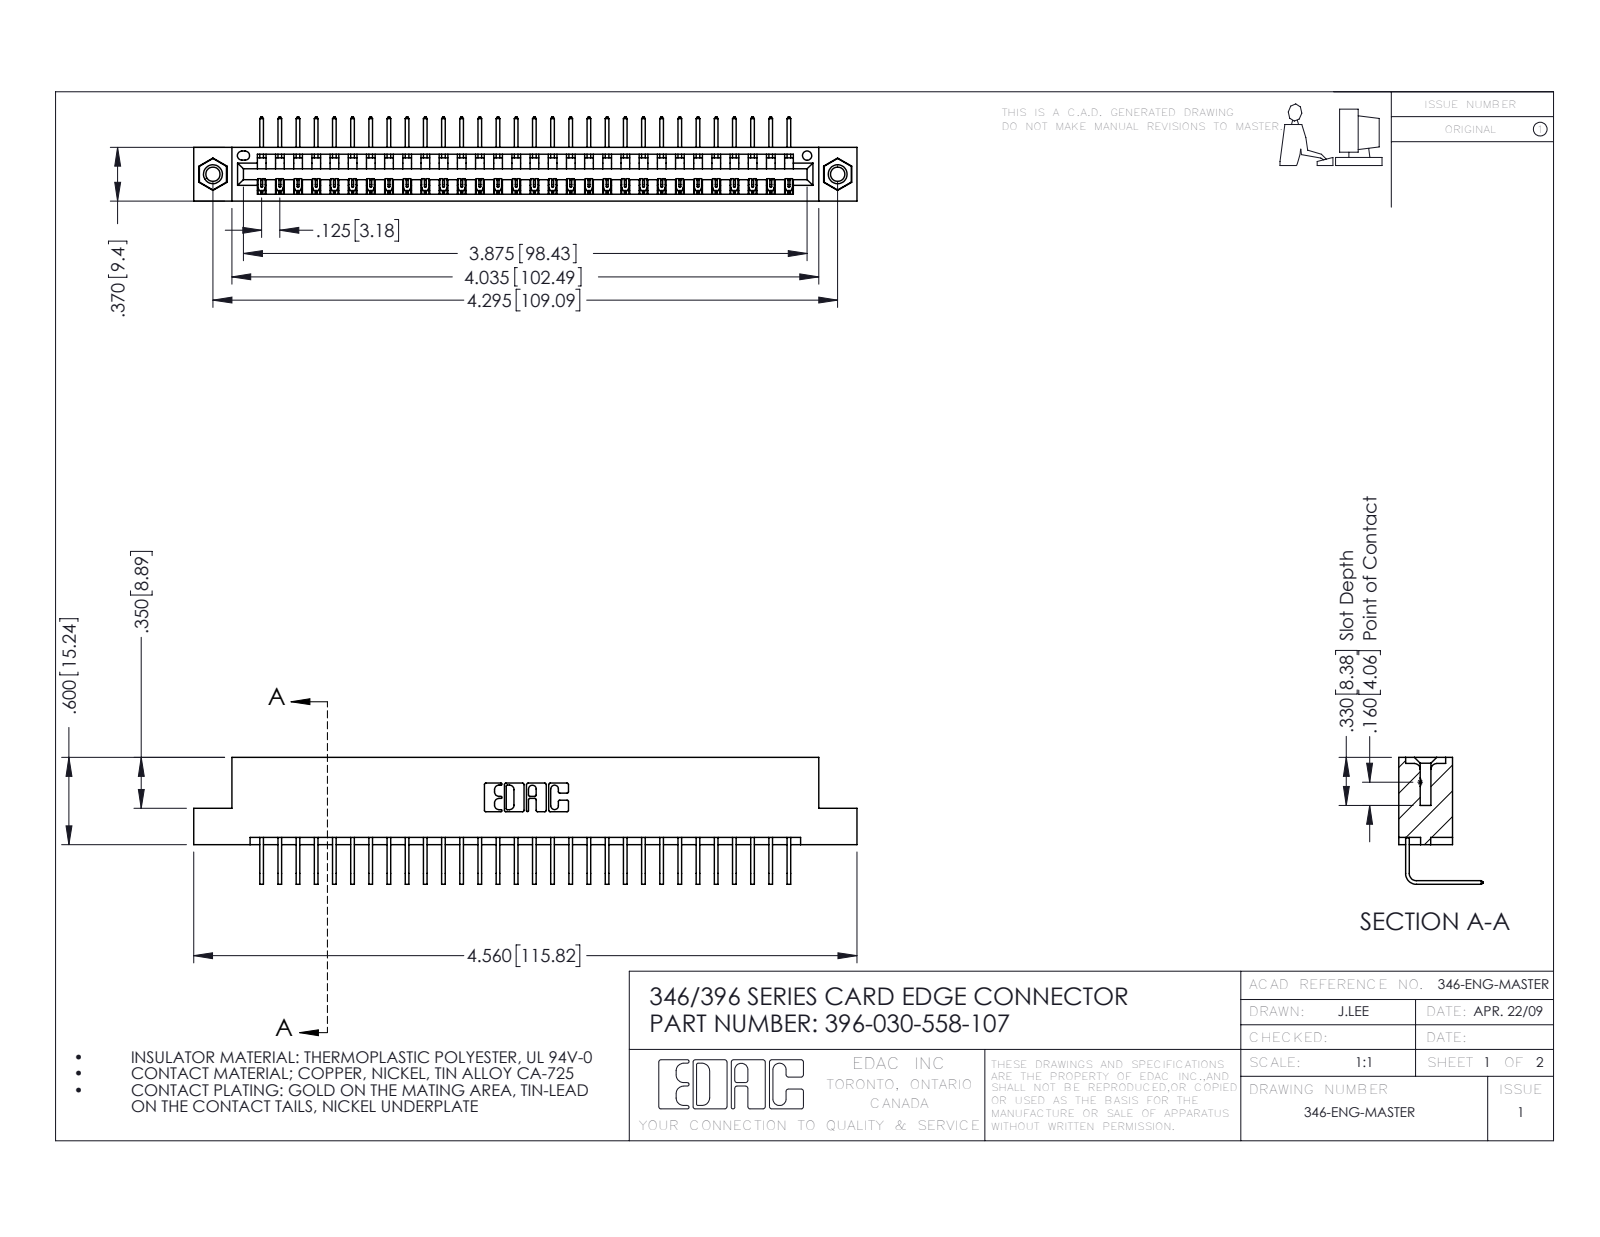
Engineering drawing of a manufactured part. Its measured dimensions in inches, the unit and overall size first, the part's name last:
Units: inches
Overall size (bounding box): 4.56 × 0.873 × 0.58
Round holes (diameter × count): ⌀0.098 ×2, ⌀0.125 ×2, ⌀0.156 ×2, ⌀0.064 ×1
Round bosses / shafts (diameter × count): ⌀0.155 ×2
Partial cylindrical surfaces — rounded edges, fillets, slot ends (radius × count): R0.006 ×60, R0.01 ×22, R0.007 ×6, R0.031 ×6, R0.026 ×3, R0.031 ×2, R0.04 ×2, R0.014 ×1
Main face-to-face distances: 0.322, 0.048, 0.37, 0.25, 0.298, 0.025, 0.072, 0.148, 0.222, 0.1
Hole centre spacings: 0.246, 4.087, 4.295
Volume: 0.677 in³ · Surface area: 22.26 in²
Bodies: 33 solids, 1982 faces (1368 planar, 598 cylindrical, 16 other)
Part name (STEP PRODUCT): 346 Part_Flush Mounting Lugs - 0.156 Dia-TI; 396-030-558-107; 345-250-001_345-250-005-103; 345-292-001_558 Tail - 2
STEP written by: SolidWorks 2016 (CONFIG_CONTROL_DESIGN)
